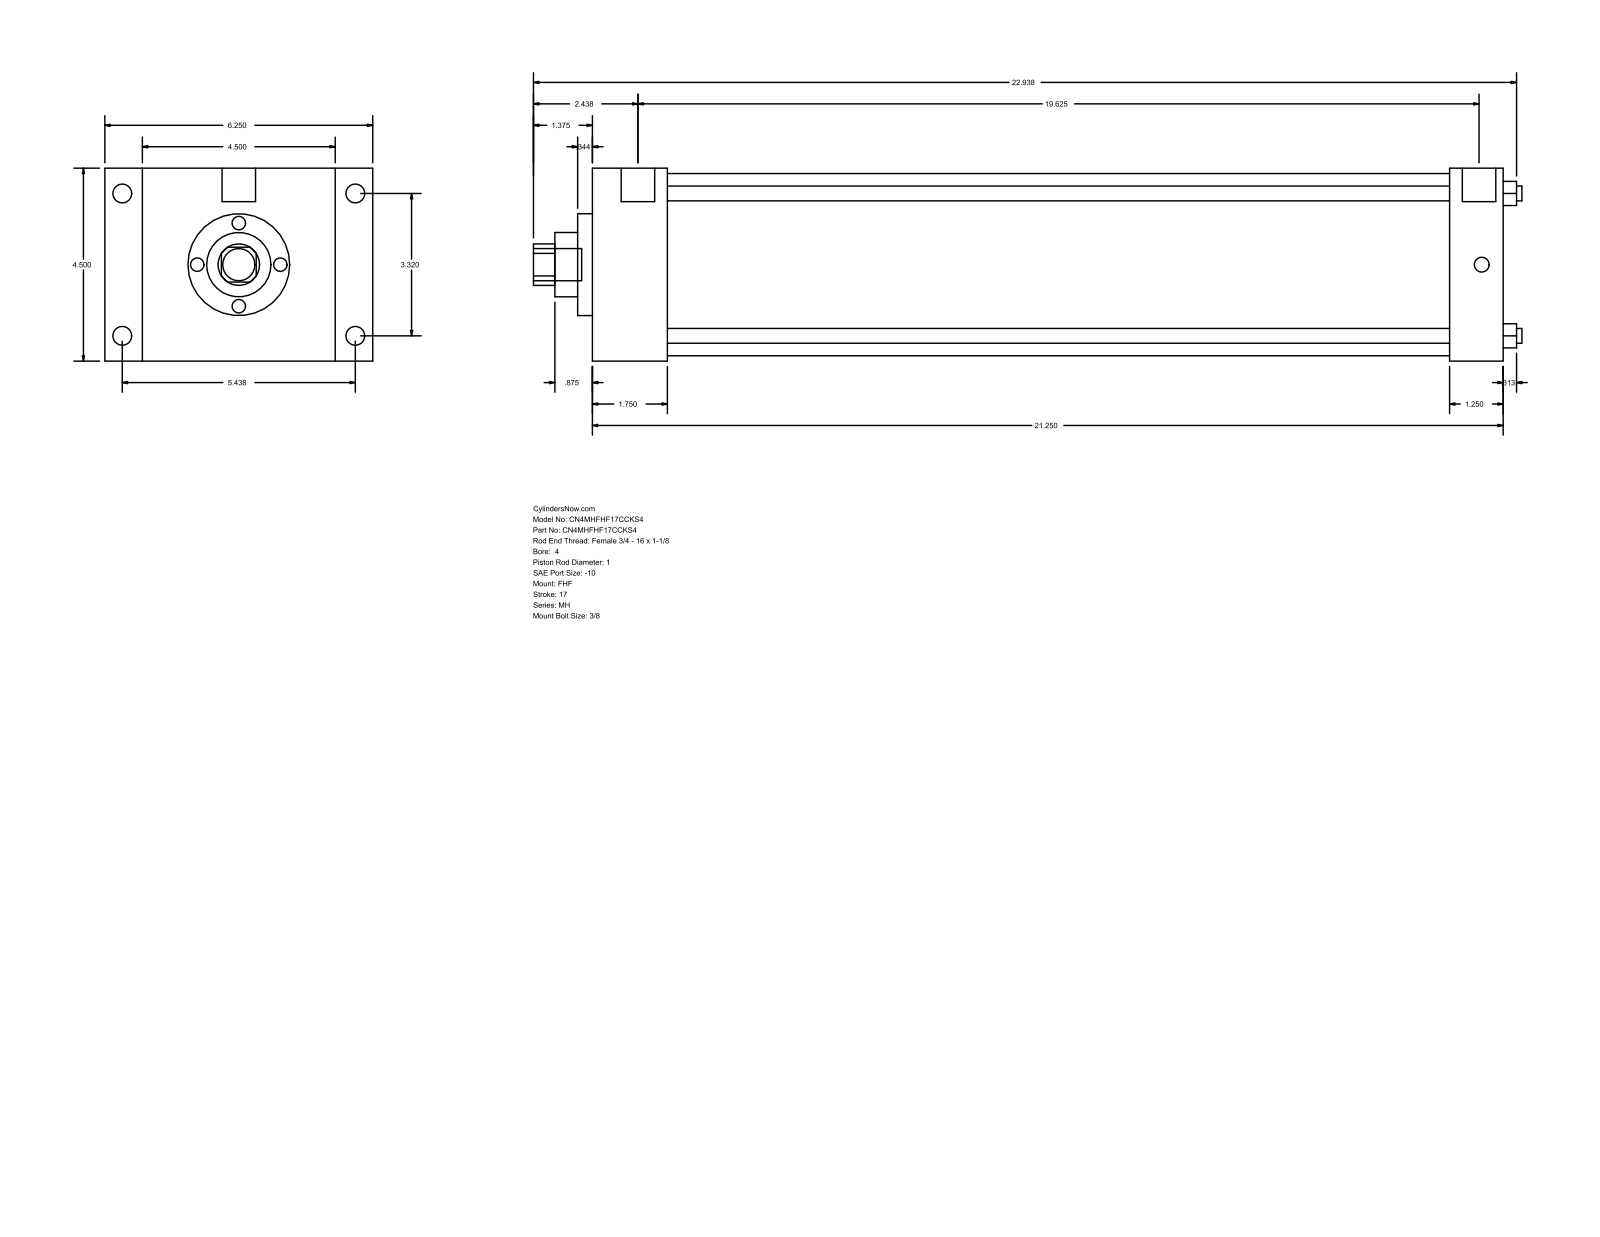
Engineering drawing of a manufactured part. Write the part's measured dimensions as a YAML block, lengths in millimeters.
part_name: "MH_FHF__0400_1"
step_written_by: "GSSL Pune (CONFIG_CONTROL_DESIGN)"
units: millimeters
bodies: {solids: 0, faces: 90, planar: 61, cylindrical: 29, other: 0}
overall_size: [585.79, 158.75, 114.3]
round_holes:
  - {diameter: 8.76, count: 4}
  - {diameter: 25.4, count: 1}
  - {diameter: 38.1, count: 1}
  - {diameter: 60.33, count: 1}
  - {diameter: 107.95, count: 1}
round_bosses_or_shafts:
  - {diameter: 11.13, count: 4}
  - {diameter: 8.73, count: 4}
  - {diameter: 19.84, count: 2}
  - {diameter: 19.05, count: 1}
partial_cylinders:
  - {radius: 12.29, count: 1}
face_to_face_distances: [114.3, 539.75, 44.46, 495.29, 22.23, 136.53, 158.76, 508, 463.54, 31.75]
hole_center_spacings: [59.62, 84.32, 119.25]
